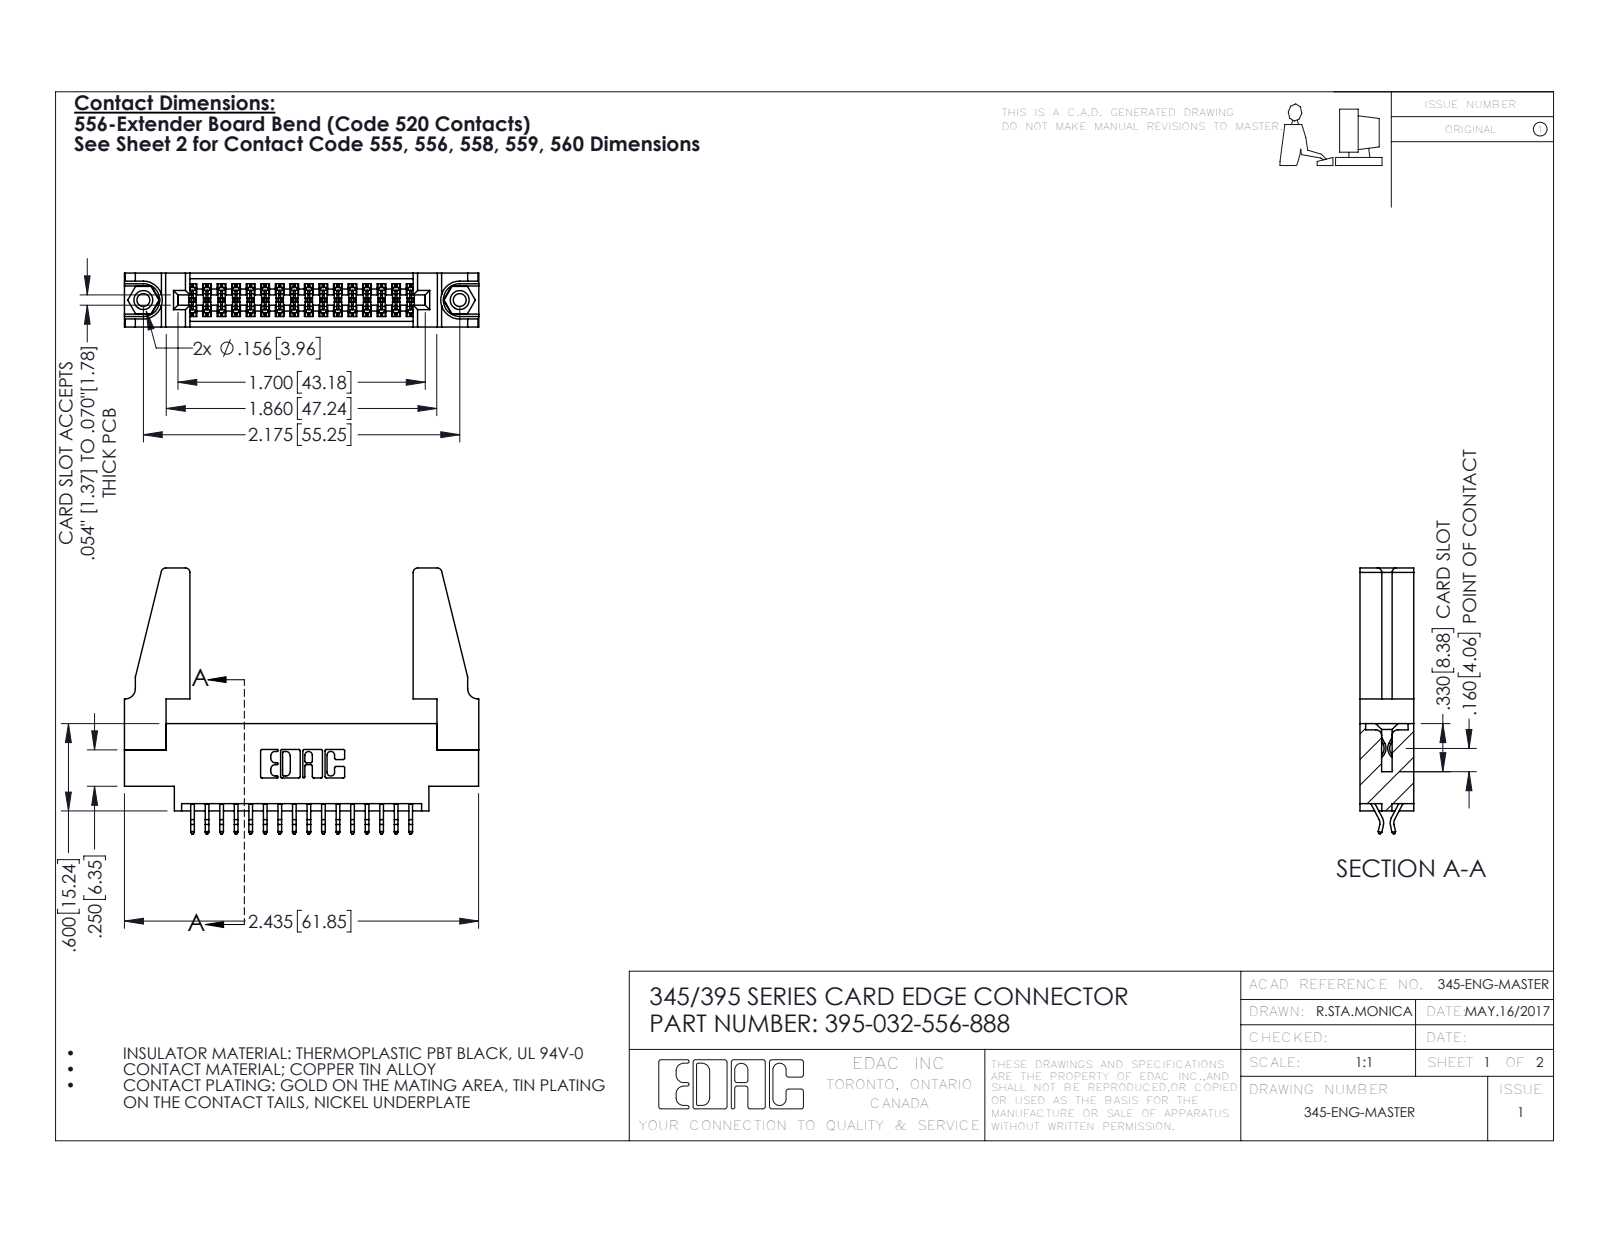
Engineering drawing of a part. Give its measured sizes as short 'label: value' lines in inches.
name: 395-032-556-888; 345-292-001_556 Tail; 345-250-001_345-250-001-102; 345 Part_0.170 Offset - 0.156 Dia-TH (+1 more)
written by: SolidWorks 2016 (CONFIG_CONTROL_DESIGN)
unit: in
bodies: 37 solids, 2046 faces (1340 planar, 690 cylindrical, 16 other)
size: 2.436 × 1.827 × 0.37
volume: 0.544 in³; area: 17.19 in²
holes: 2× ⌀0.089, 2× ⌀0.125, 2× ⌀0.156, 1× ⌀0.064
bosses: 2× ⌀0.155
rounds: 48× R0.006, 22× R0.01, 8× R0.03, 6× R0.007, 6× R0.031, 3× R0.026, 2× R0.01, 2× R0.014
face distances: 0.37, 0.072, 0.298, 0.2, 0.025, 0.098, 0.272, 0.225, 0.175, 0.148
hole spacings: 0.27, 1.942, 2.175
